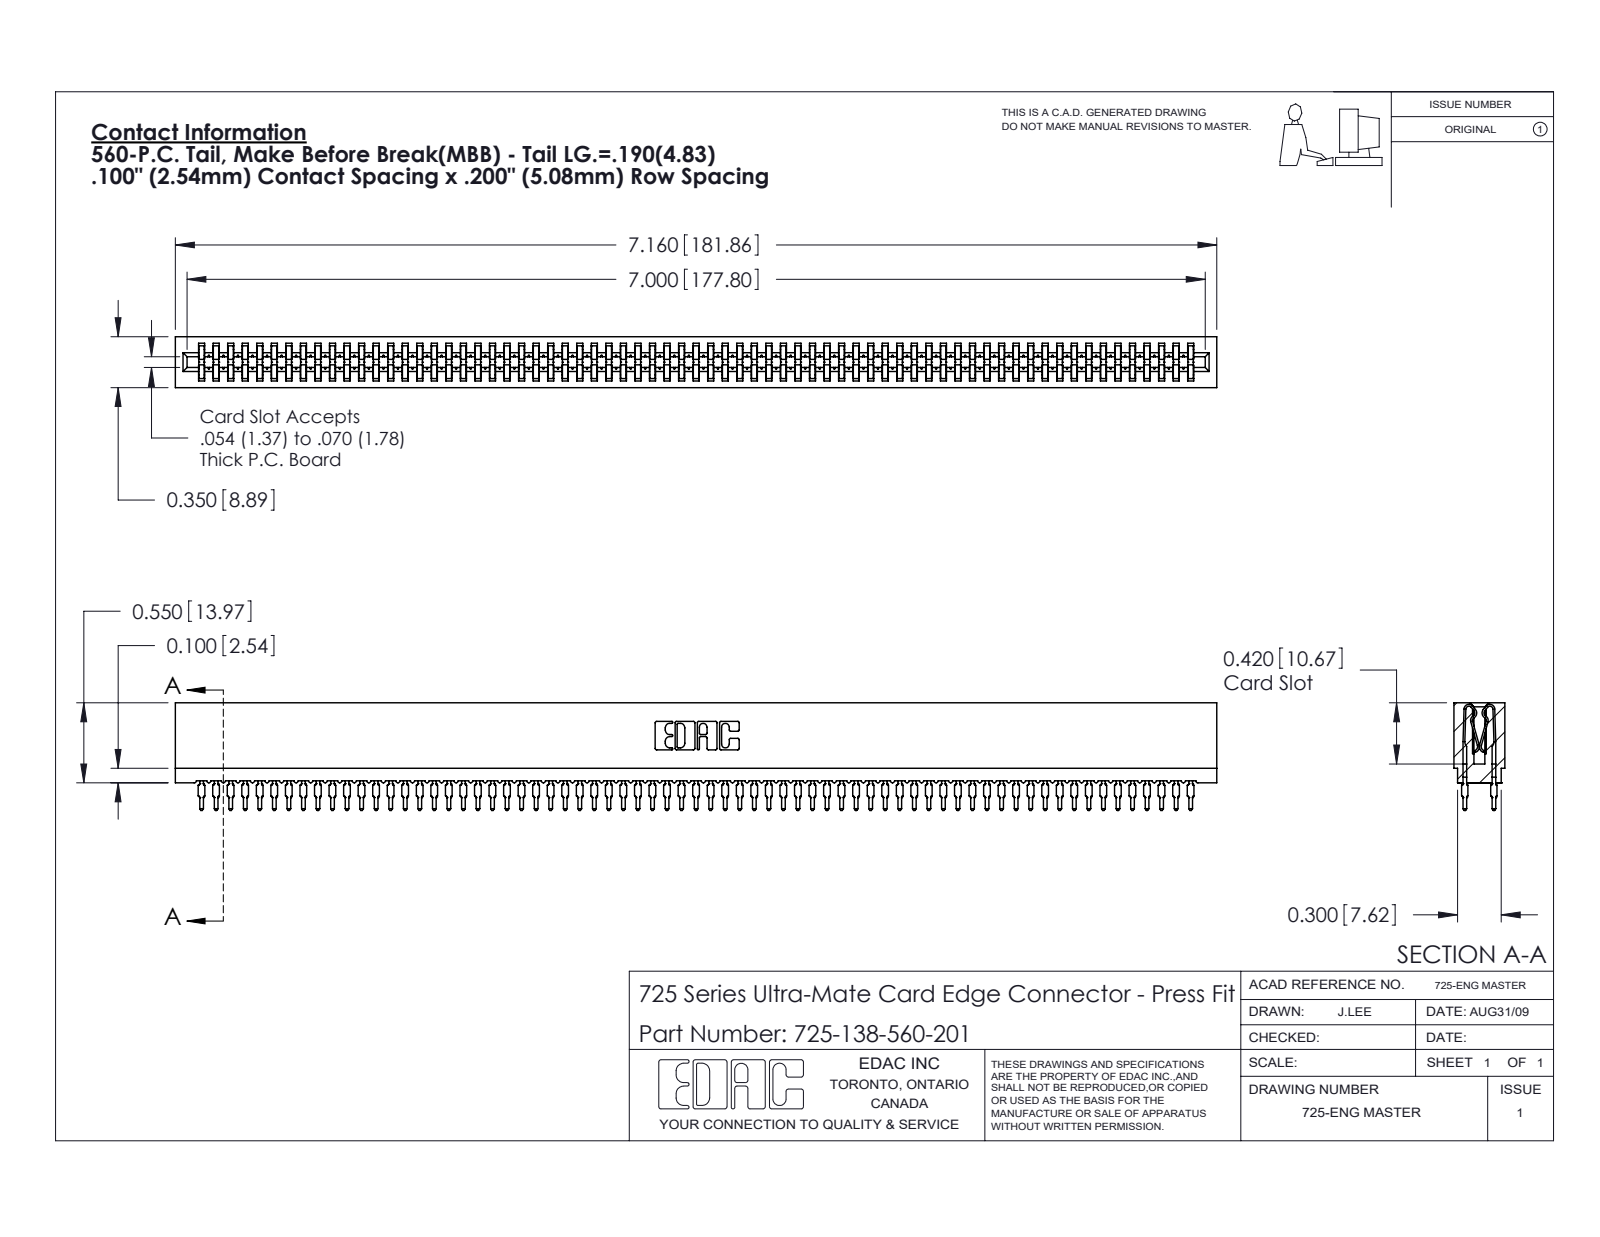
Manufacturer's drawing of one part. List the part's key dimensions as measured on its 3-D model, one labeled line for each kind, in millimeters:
Part name (STEP PRODUCT): 745-292-001_560; 725-138-560-201; 725 Part_Insulator Option - 01
STEP written by: SolidWorks 2020 (CONFIG_CONTROL_DESIGN)
Units: millimetres
Bodies: 139 solids, 13688 faces (7093 planar, 3007 cylindrical, 3588 other)
Overall size (bounding box): 181.9 × 18.8 × 8.9
Volume: 14 800 mm³ · Surface area: 34 010 mm²
Partial cylindrical surfaces — rounded edges, fillets, slot ends (radius × count): R0.5 ×276, R0.4 ×138, R0.3 ×22, R0.1 ×8, R0.3 ×8, R0.2 ×6, R0.8 ×6, R0.7 ×3
Main face-to-face distances: 1.6, 7.3, 8.9, 5.4, 3.5, 1.9, 3.8, 5.1, 1.1, 7.7
